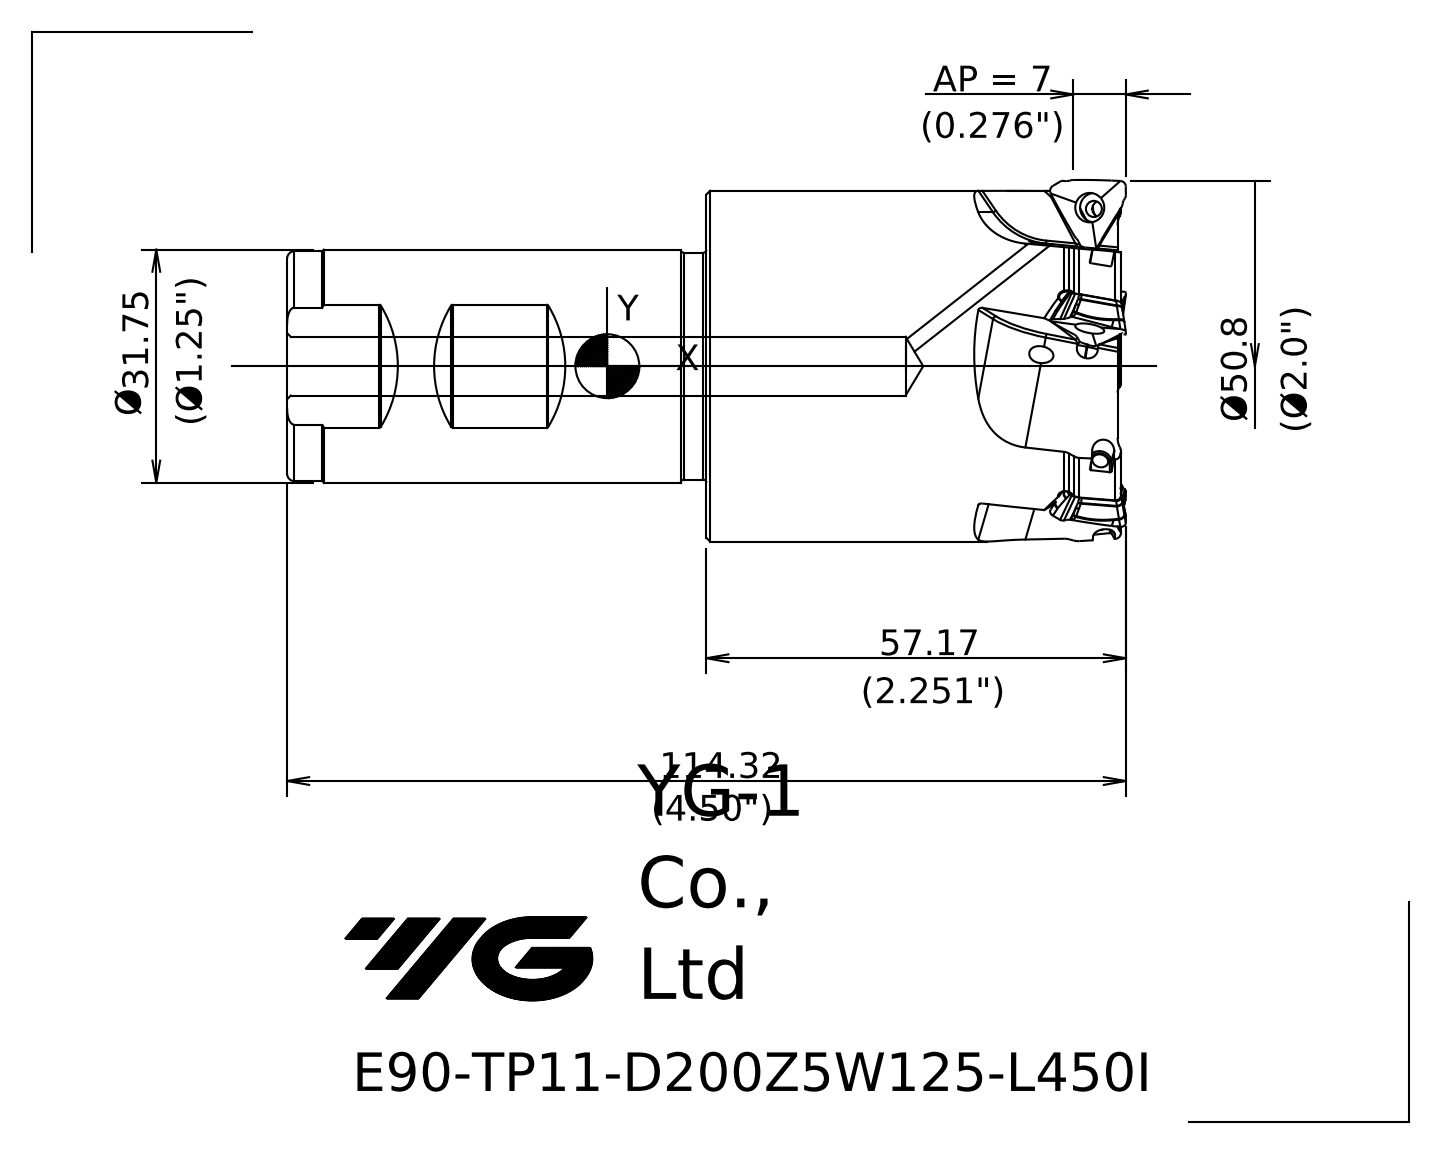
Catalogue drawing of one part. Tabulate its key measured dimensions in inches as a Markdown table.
| quantity | value |
| --- | --- |
| part name | 10222DA0A397nvph |
| STEP written by | SIEMENS PLM Software NX 10.0 (AP203_CONFIGURATION_CONTROLLED_3D_DESIGN_OF_MECHANICAL_PARTS_AND_ASSEMBLIES_MIM_LF) |
| units | inches |
| bodies | 1 solid, 73 faces (9 planar, 19 cylindrical, 45 other) |
| overall size | 4.501 × 2.004 × 2.004 |
| volume | 8.56 in³ |
| surface area | 39.26 in² |
| round holes (diameter × count) | 0.079 × 5, 0.094 × 5, 0.059 × 1, 0.315 × 1 |
| round bosses / shafts (diameter × count) | 1.882 × 1, 1.25 × 1, 1.234 × 1, 1.219 × 1 |
| partial cylindrical surfaces (radius × count) | 0.012 × 3 |
| main face-to-face distances | 2.207, 4.457, 2.25, 0.016, 2.222, 4.472, 0.635 |
